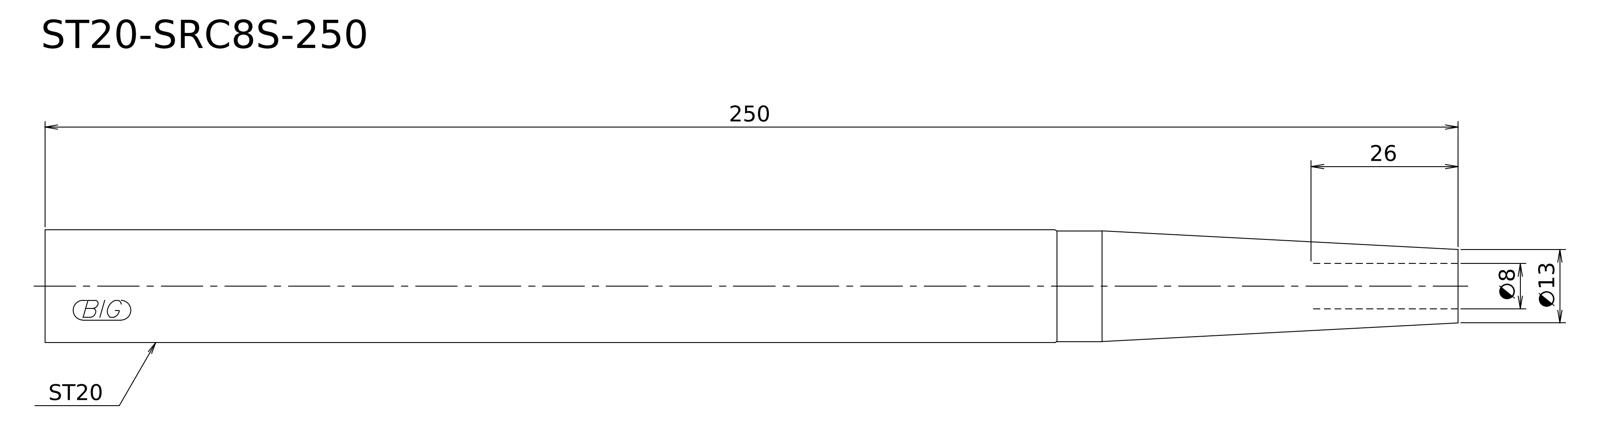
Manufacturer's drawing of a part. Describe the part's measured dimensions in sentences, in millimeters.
Its 3-D file was written by "Kubotek KeyCreator V8.5.1 (14335) (CONFIG_CONTROL_DESIGN)". It is 1 solid with 6 faces: 2 planar, 2 cylindrical and 2 other. Overall it measures 250 by 20 by 20 millimeters. Its volume is 71 975 cubic millimeters and its surface area 15 420 square millimeters. Round bosses or shafts: 1 of diameter 20, 1 of diameter 19.6. The main face-to-face distances are 250.
